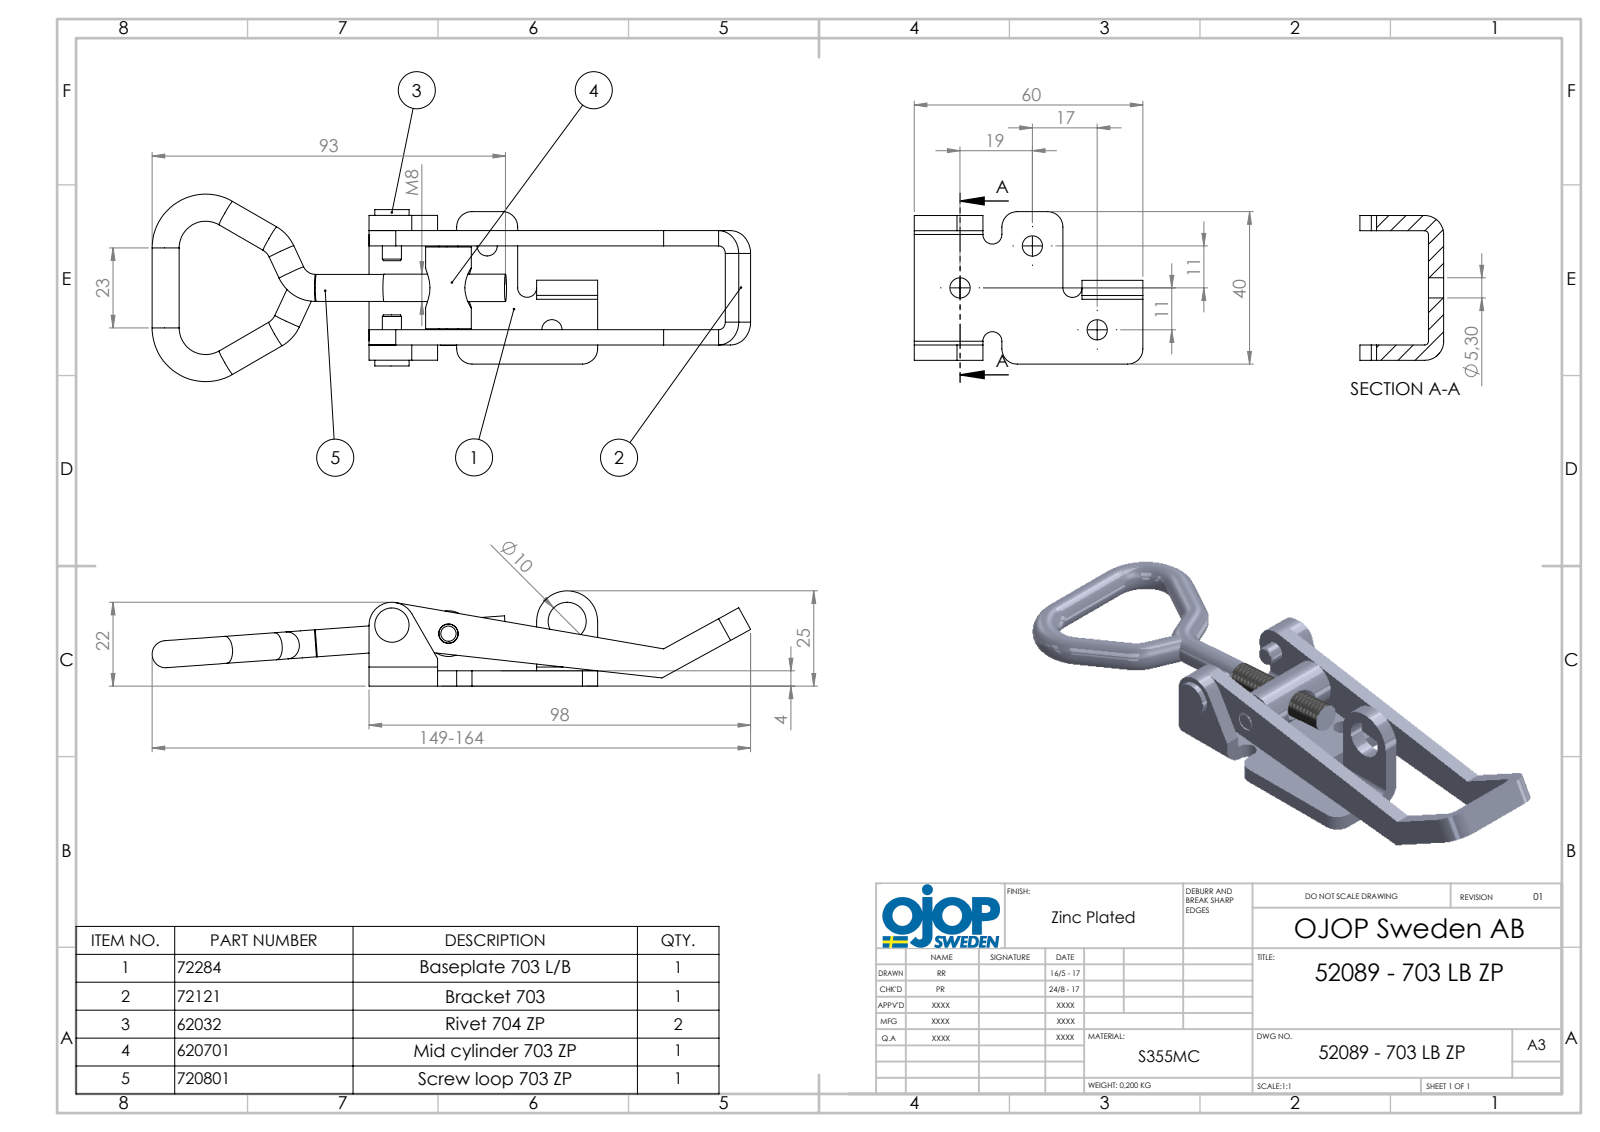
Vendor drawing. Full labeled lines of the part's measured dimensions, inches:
Part name (STEP PRODUCT): 703 - Skruvögla; 703 - Bygel; 703 - Rulle; 704 - Rivet Gradin (+2 more)
STEP written by: SolidWorks 2015 (AUTOMOTIVE_DESIGN)
Units: inches
Bodies: 6 solids, 168 faces (66 planar, 72 cylindrical, 30 other)
Overall size (bounding box): 6.446 × 1.945 × 0.984
Volume: 1.652 in³ · Surface area: 28.64 in²
Round holes (diameter × count): ⌀0.209 ×3, ⌀0.201 ×2, ⌀0.283 ×1, ⌀0.303 ×1, ⌀0.394 ×1
Round bosses / shafts (diameter × count): ⌀0.276 ×4, ⌀0.197 ×2, ⌀0.472 ×1, ⌀0.354 ×1, ⌀0.303 ×1
Partial cylindrical surfaces — rounded edges, fillets, slot ends (radius × count): R0.157 ×4, R0.039 ×3, R0.098 ×3, R0.197 ×3, R0.236 ×3, R0.079 ×2, R0.315 ×1
Main face-to-face distances: 0.157, 1.024, 1.181, 0.866, 0.669, 0.512, 0.354, 0.827, 0.315, 1.339
Hole centre spacings: 0.591, 0.864, 1.094, 1.233, 1.482, 1.811
